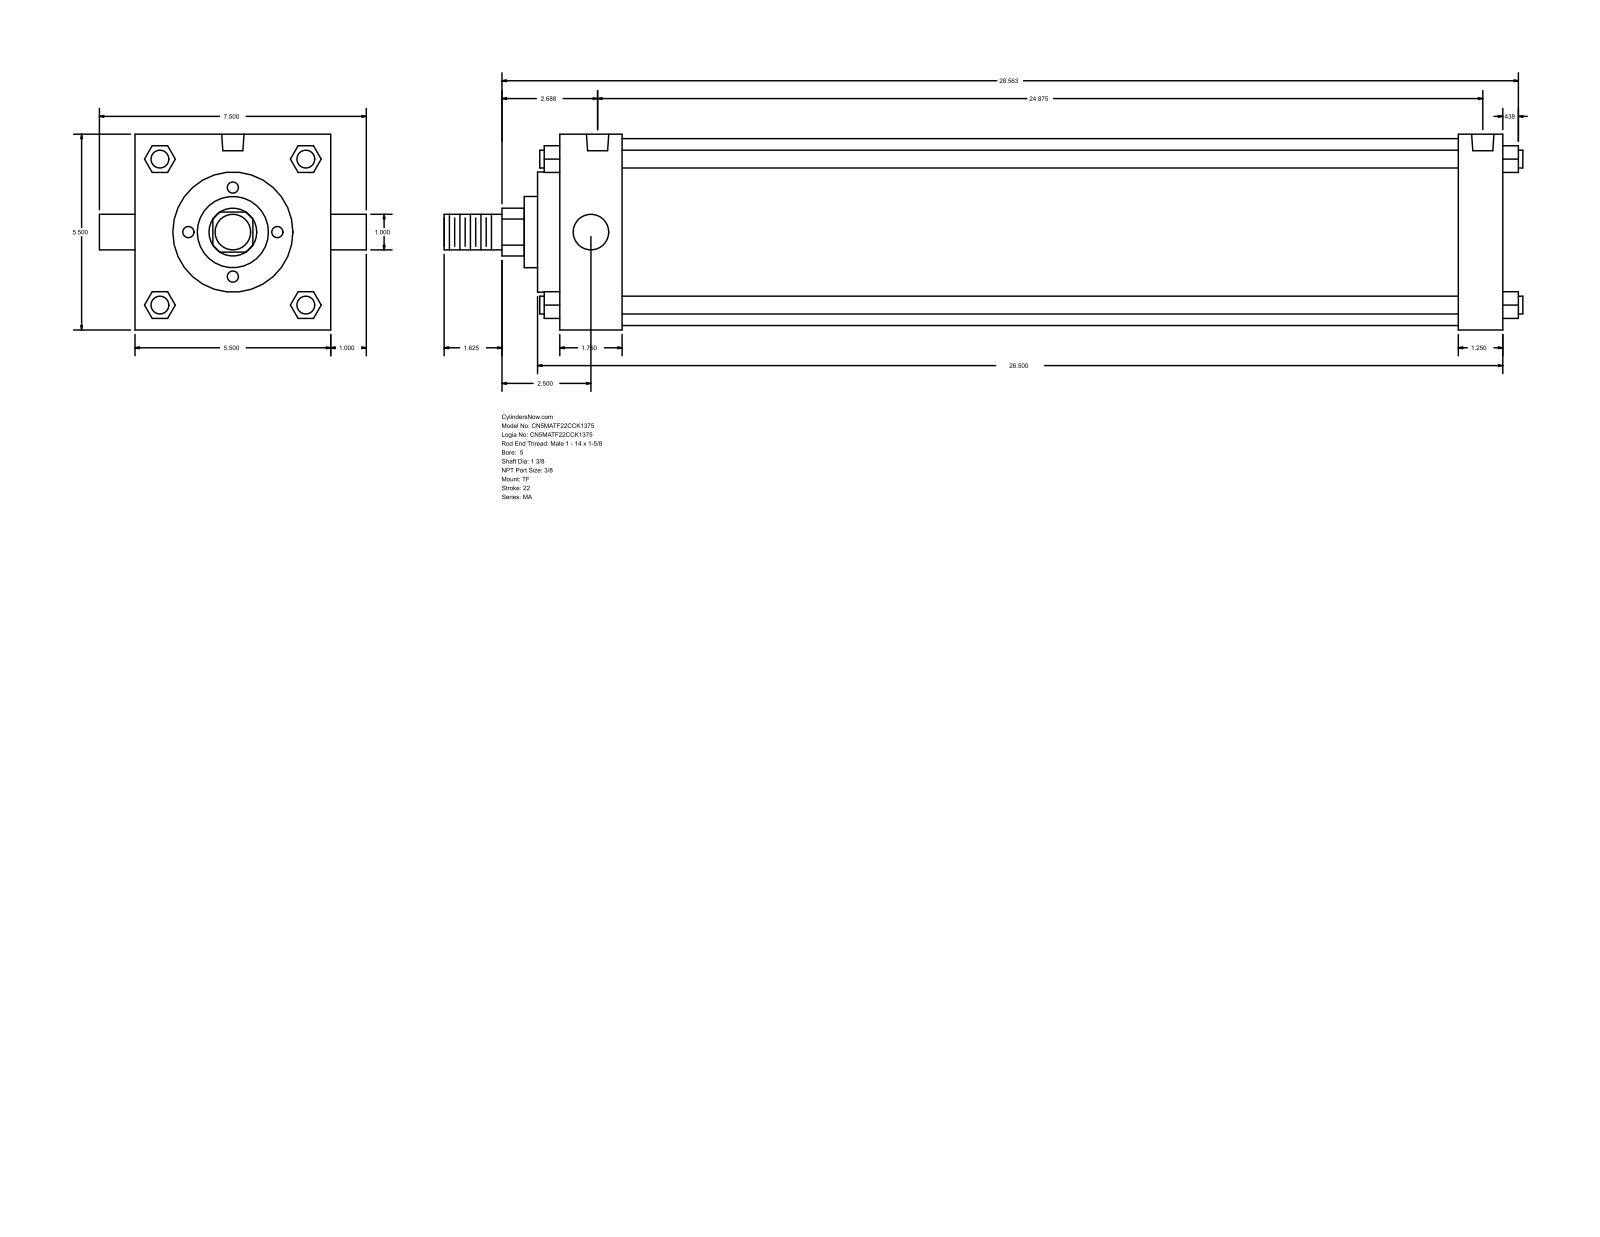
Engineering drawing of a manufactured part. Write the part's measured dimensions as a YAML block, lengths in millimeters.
part_name: "MA_TF__0500_1.375"
step_written_by: "GSSL Pune (CONFIG_CONTROL_DESIGN)"
units: millimeters
bodies: {solids: 0, faces: 122, planar: 93, cylindrical: 29, other: 0}
overall_size: [769.94, 190.5, 139.7]
round_holes:
  - {diameter: 11.11, count: 3}
  - {diameter: 15.93, count: 2}
round_bosses_or_shafts:
  - {diameter: 12.7, count: 4}
  - {diameter: 25.4, count: 2}
  - {diameter: 133.35, count: 1}
  - {diameter: 85.72, count: 1}
  - {diameter: 50.8, count: 1}
  - {diameter: 34.92, count: 1}
partial_cylinders:
  - {radius: 17.06, count: 1}
face_to_face_distances: [139.7, 673.11, 641.35, 31.76, 44.45, 596.9, 628.66, 15.87, 60.32, 657.22]
hole_center_spacings: [4.76, 4.77, 622.3, 627.06, 627.07, 631.83]
